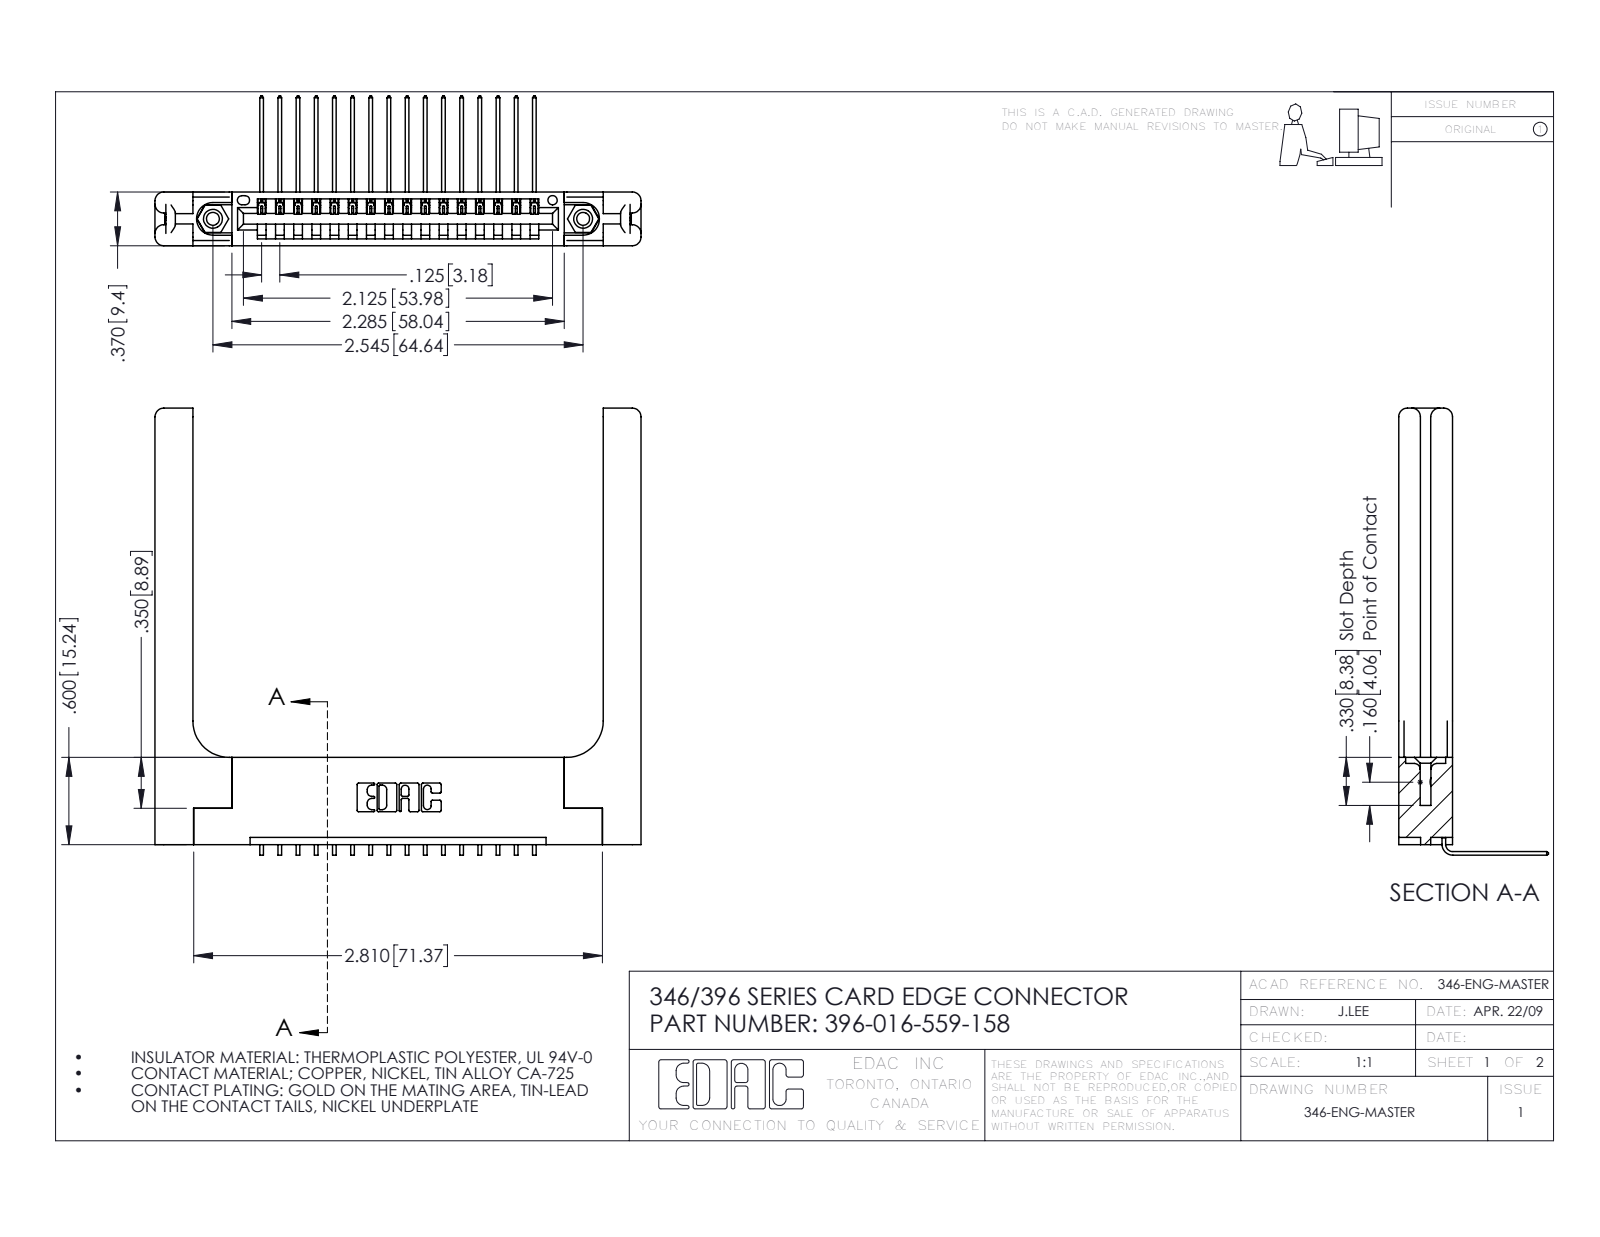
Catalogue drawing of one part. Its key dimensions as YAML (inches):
part_name: "346 Part_Flush Mounting Lugs - 0.156 Dia-TH; 345-292-001_558 559 Tail - 1; 396-016-559-158; 346-220-058_345-220-058 (+1 more)"
step_written_by: "SolidWorks 2016 (CONFIG_CONTROL_DESIGN)"
units: inches
bodies: {solids: 21, faces: 1338, planar: 896, cylindrical: 382, other: 60}
overall_size: [3.341, 3.073, 1.03]
volume: 0.947
surface_area: 23.56
round_holes:
  - {diameter: 0.089, count: 2}
  - {diameter: 0.125, count: 2}
  - {diameter: 0.156, count: 2}
  - {diameter: 0.064, count: 1}
round_bosses_or_shafts:
  - {diameter: 0.155, count: 2}
partial_cylinders:
  - {radius: 0.006, count: 32}
  - {radius: 0.01, count: 22}
  - {radius: 0.06, count: 16}
  - {radius: 0.007, count: 6}
  - {radius: 0.031, count: 6}
  - {radius: 0.026, count: 3}
  - {radius: 0.03, count: 2}
  - {radius: 0.031, count: 2}
face_to_face_distances: [0.37, 0.072, 0.15, 0.322, 0.048, 0.148, 0.25, 0.102, 0.22, 0.173]
hole_center_spacings: [0.246, 2.338, 2.545]
